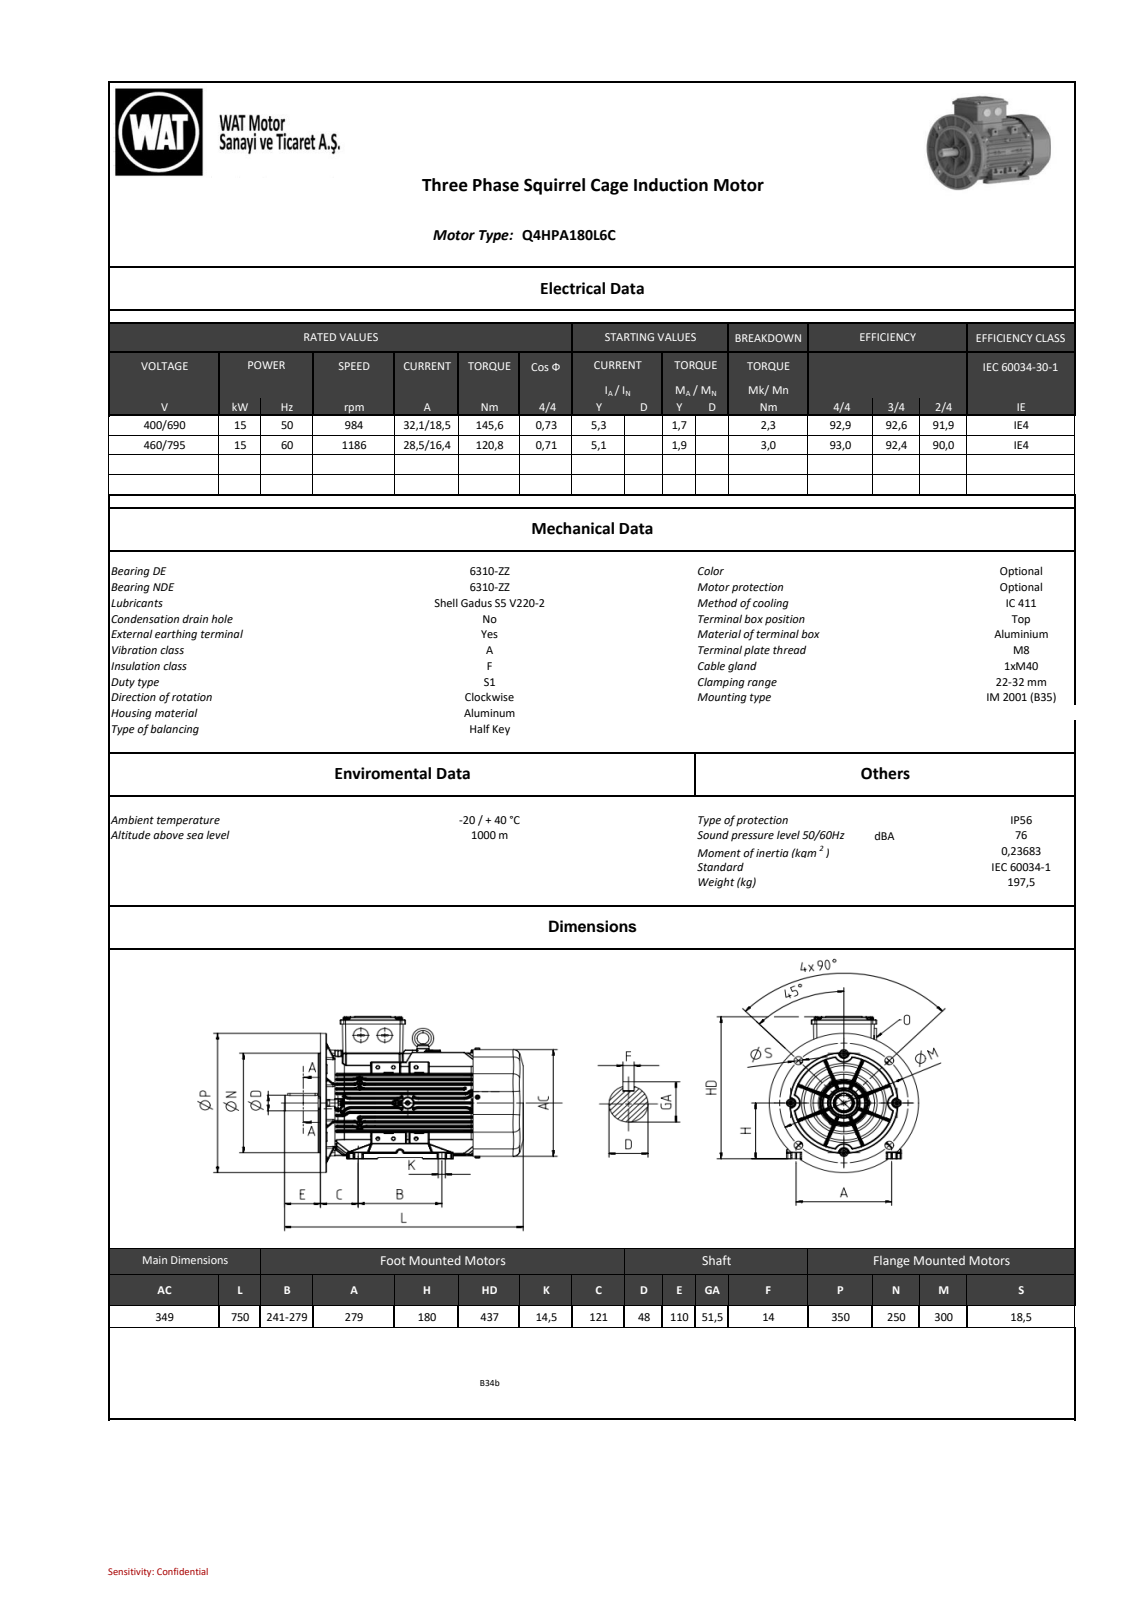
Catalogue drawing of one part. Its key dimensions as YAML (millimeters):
part_name: "001_objects"
step_written_by: "SIEMENS PLM Software NX2206.8101 (AP203_CONFIGURATION_CONTROLLED_3D_DESIGN_OF_MECHANICAL_PARTS_AND_ASSEMBLIES_MIM_LF)"
units: millimeters
bodies: {solids: 0, faces: 7437, planar: 2473, cylindrical: 2698, other: 2266}
overall_size: [749.5, 433, 351.36]
round_holes:
  - {diameter: 5.6, count: 4}
  - {diameter: 17, count: 4}
  - {diameter: 18.5, count: 4}
  - {diameter: 22, count: 2}
  - {diameter: 25.05, count: 2}
  - {diameter: 5.5, count: 1}
  - {diameter: 6.65, count: 1}
  - {diameter: 8, count: 1}
  - {diameter: 51, count: 1}
  - {diameter: 80, count: 1}
  - {diameter: 82, count: 1}
  - {diameter: 110, count: 1}
round_bosses_or_shafts:
  - {diameter: 9.5, count: 3}
  - {diameter: 55, count: 2}
  - {diameter: 51.2, count: 2}
  - {diameter: 25, count: 2}
  - {diameter: 20, count: 2}
  - {diameter: 18.1, count: 2}
  - {diameter: 16, count: 2}
  - {diameter: 13, count: 2}
partial_cylinders:
  - {radius: 2, count: 851}
  - {radius: 1, count: 699}
  - {radius: 5, count: 130}
  - {radius: 3, count: 44}
  - {radius: 4, count: 40}
  - {radius: 8, count: 22}
  - {radius: 0.5, count: 18}
  - {radius: 1, count: 18}
face_to_face_distances: [1.2, 16.21, 5, 32.48, 16.27, 171.05, 173.83, 141.35, 157.62, 157.07]
hole_center_spacings: [119.45, 287.36, 150.01, 161, 212.14, 227.69, 300.01, 322]
